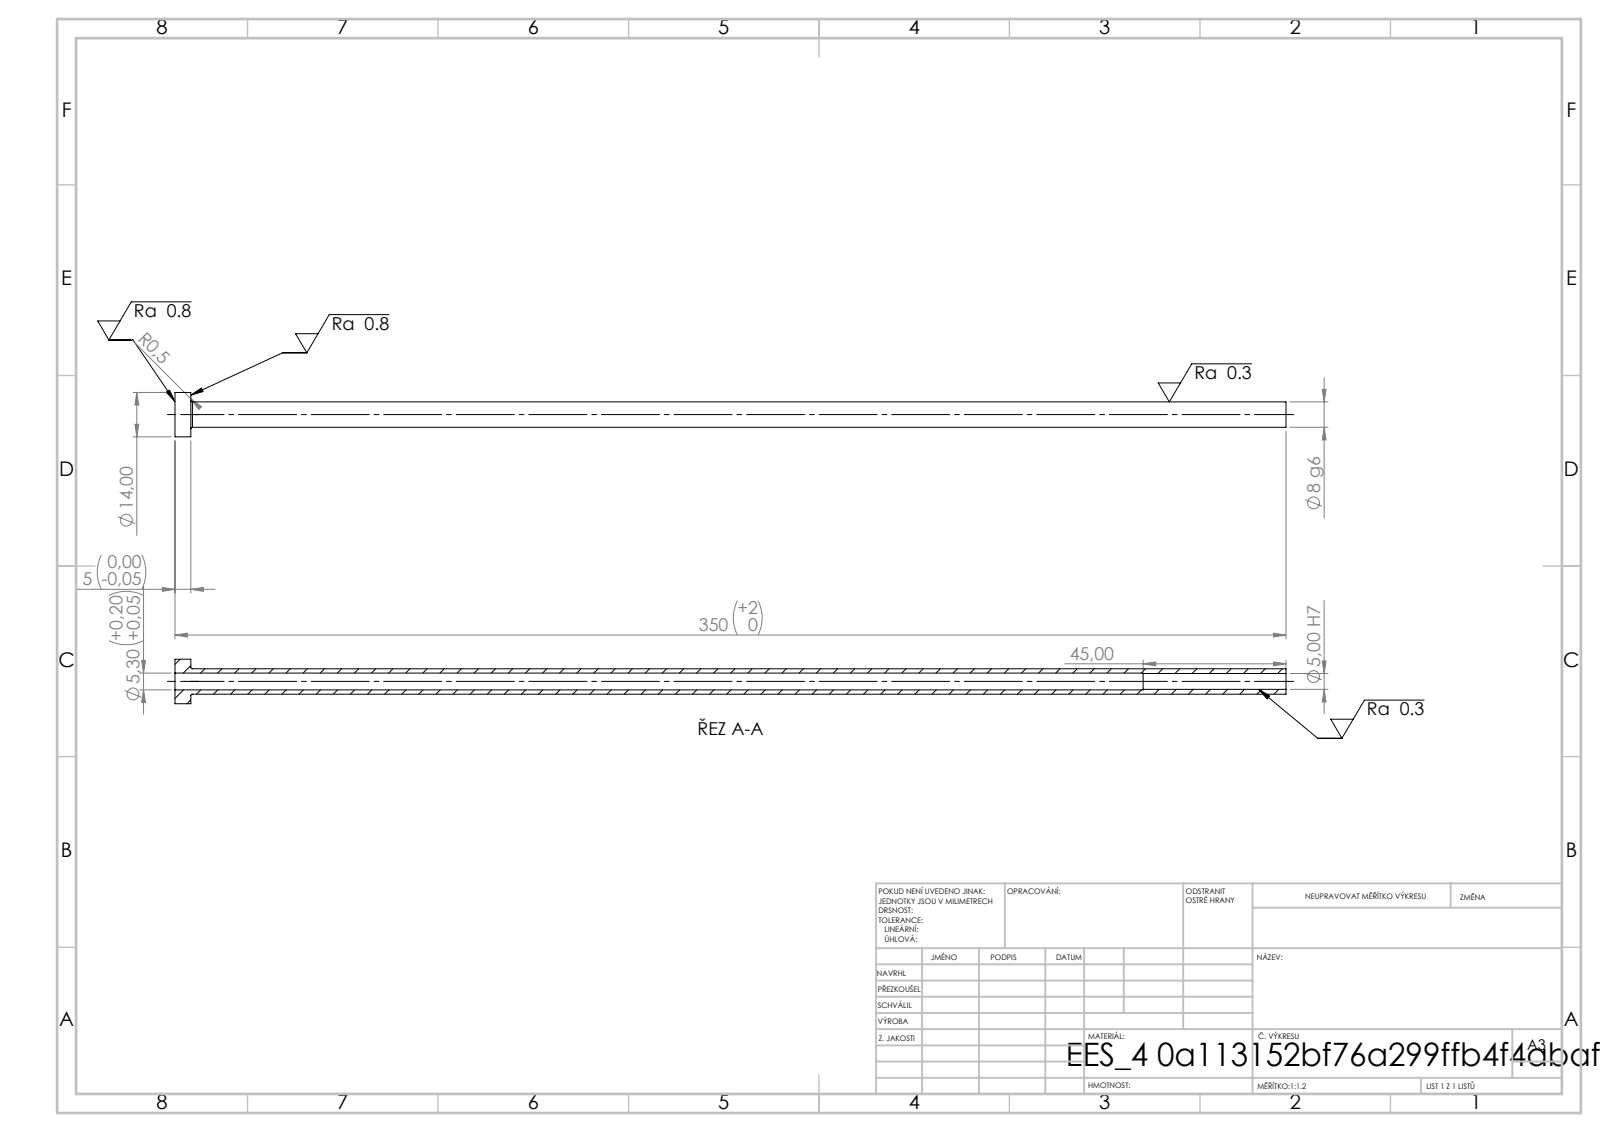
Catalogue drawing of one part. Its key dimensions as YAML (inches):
step_written_by: "SolidWorks 2019 (CONFIG_CONTROL_DESIGN)"
units: inches
bodies: {solids: 1, faces: 14, planar: 4, cylindrical: 8, other: 2}
overall_size: [13.78, 0.551, 0.551]
volume: 0.641
surface_area: 23.16
round_holes:
  - {diameter: 0.197, count: 1}
  - {diameter: 0.209, count: 1}
round_bosses_or_shafts:
  - {diameter: 0.551, count: 1}
  - {diameter: 0.315, count: 1}
face_to_face_distances: [0.197, 13.78, 13.583, 12.008, 11.811, 1.772]
